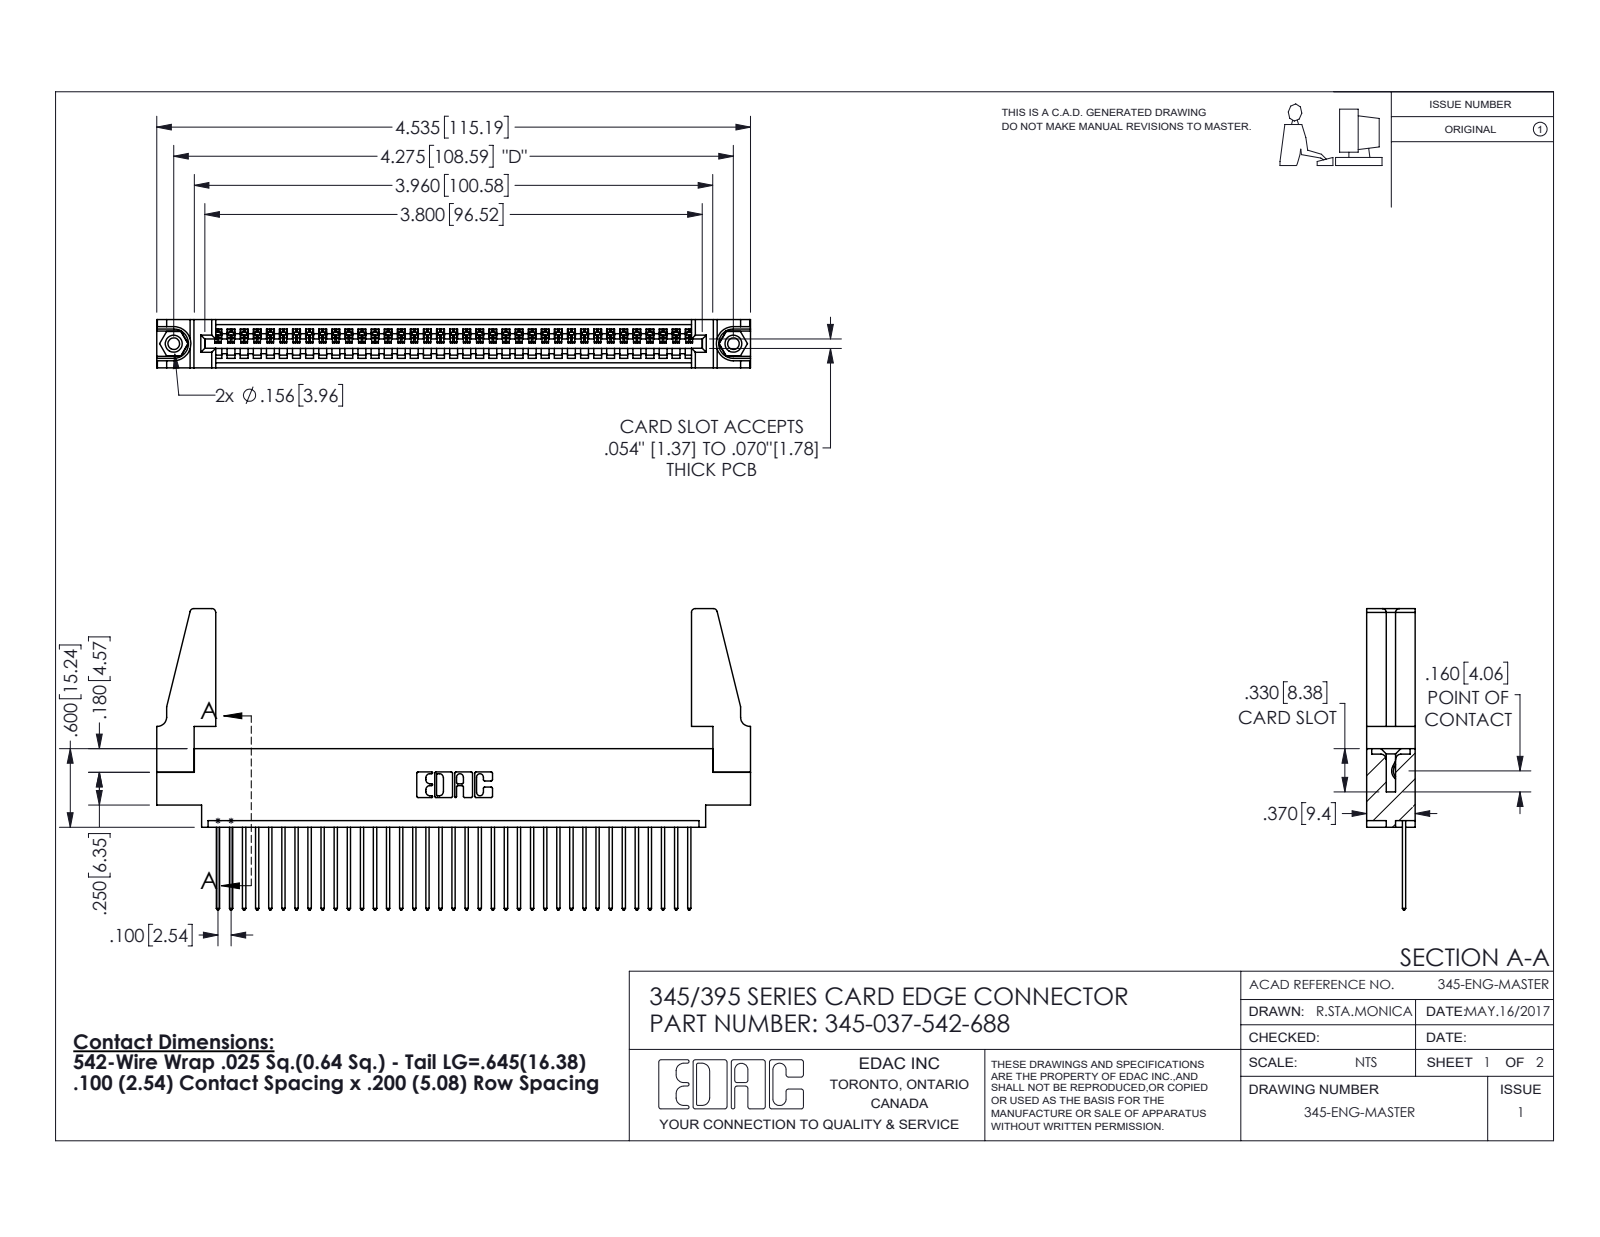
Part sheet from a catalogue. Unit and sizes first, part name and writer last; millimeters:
Units: millimetres
Overall size (bounding box): 115.2 × 58.5 × 9.4
Round holes (diameter × count): ⌀2.3 ×2, ⌀3.2 ×2, ⌀4 ×2, ⌀1.6 ×1
Round bosses / shafts (diameter × count): ⌀3.9 ×2
Partial cylindrical surfaces — rounded edges, fillets, slot ends (radius × count): R0.2 ×74, R0.3 ×74, R0.3 ×22, R0.8 ×8, R0.2 ×6, R0.8 ×6, R0.7 ×3, R0.8 ×2
Main face-to-face distances: 1.8, 7.6, 9.4, 2.5, 6.9, 0.6, 5.1, 5.7, 4.4, 3.8
Hole centre spacings: 6.9, 102.6, 108.6
Volume: 14 100 mm³ · Surface area: 18 150 mm²
Bodies: 42 solids, 2400 faces (1636 planar, 748 cylindrical, 16 other)
Part name (STEP PRODUCT): 345-220-078_345-220-088; 345-037-542-688; 345-250-001_345-250-001-102; 345-292-001_345-293-142 (+1 more)
STEP written by: SolidWorks 2016 (CONFIG_CONTROL_DESIGN)
